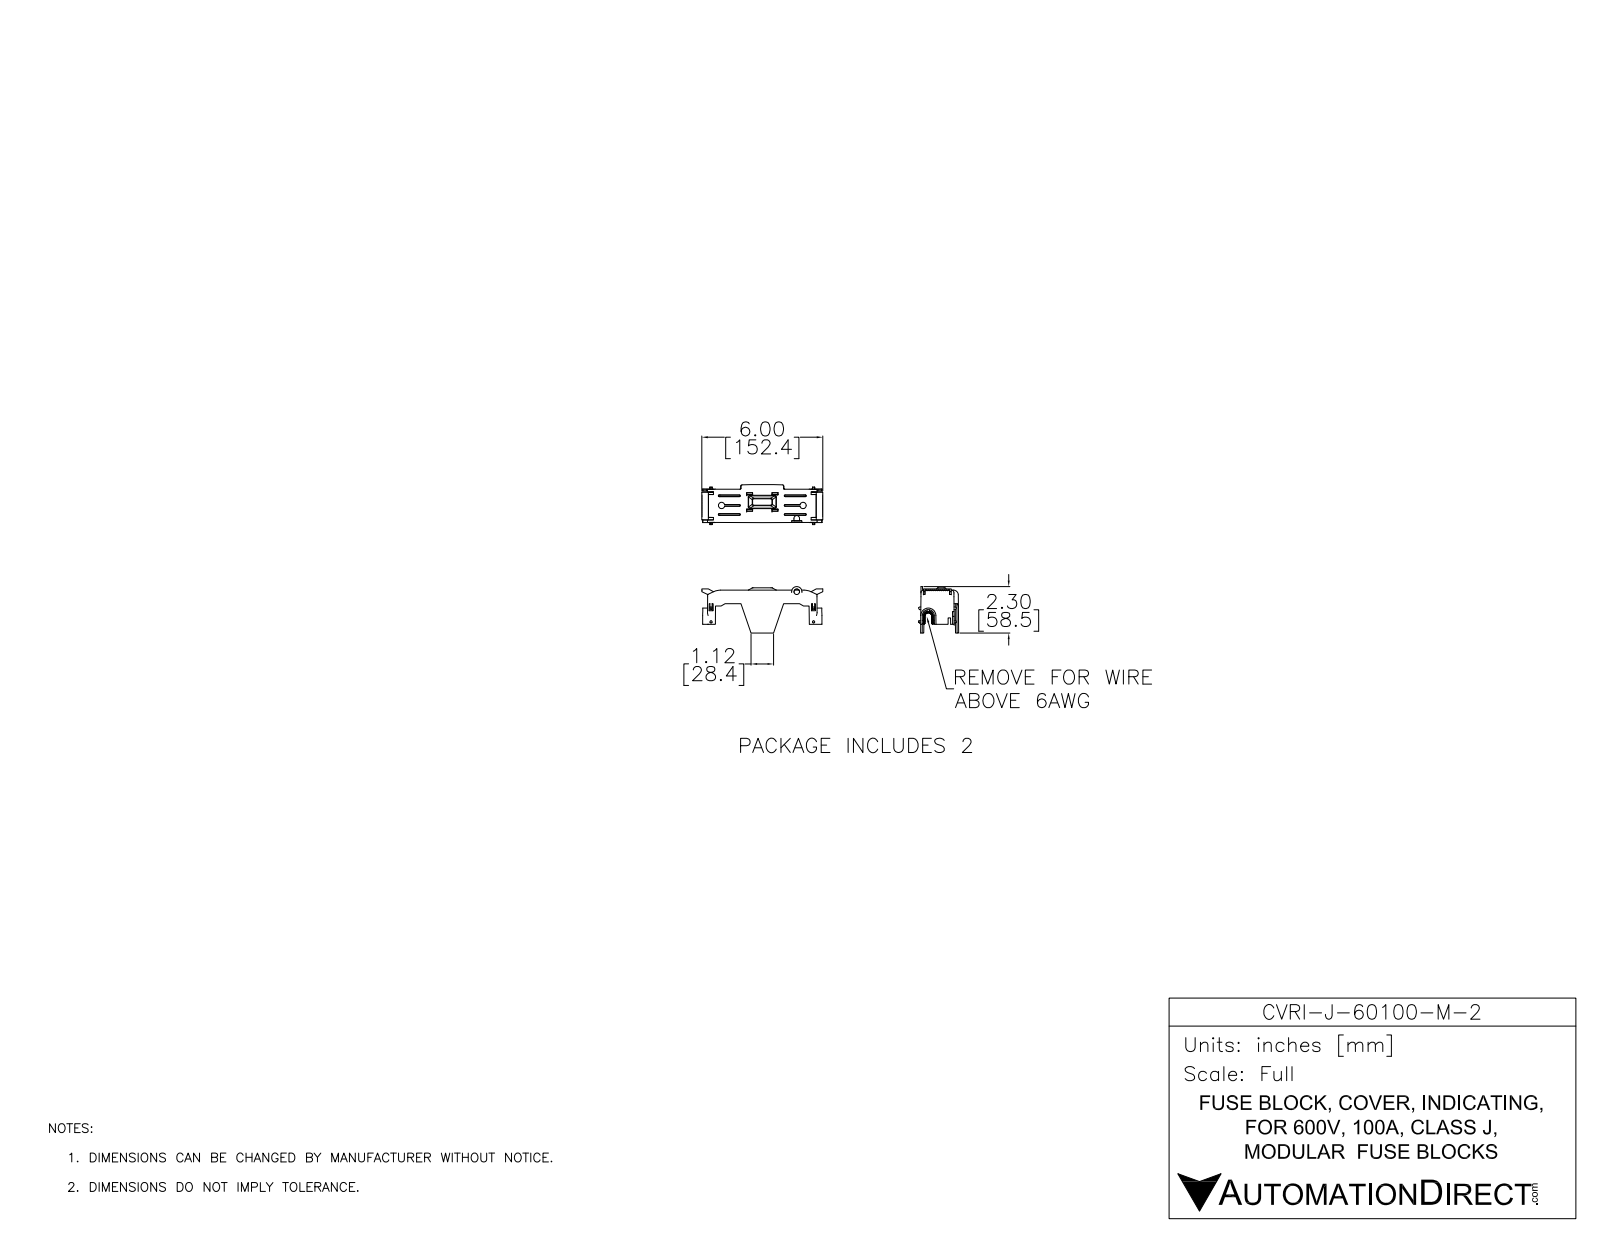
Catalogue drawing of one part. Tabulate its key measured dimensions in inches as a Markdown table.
| quantity | value |
| --- | --- |
| part name | CVRI-J-60100-M-2 |
| STEP written by | SolidWorks 2017 (AUTOMOTIVE_DESIGN) |
| units | inches |
| bodies | 1 solid, 1410 faces (917 planar, 102 cylindrical, 391 other) |
| overall size | 5.979 × 2.304 × 1.984 |
| volume | 2.55 in³ |
| surface area | 70.01 in² |
| partial cylindrical surfaces (radius × count) | 0.039 × 19, 0.118 × 14, 0.031 × 6, 0.059 × 4, 0.01 × 2, 0.02 × 2, 0.138 × 2, 0.169 × 2 |
| main face-to-face distances | 0.079, 0.217, 0.138, 0.295, 0.118, 0.347, 0.197, 0.236, 0.14, 0.061 |
